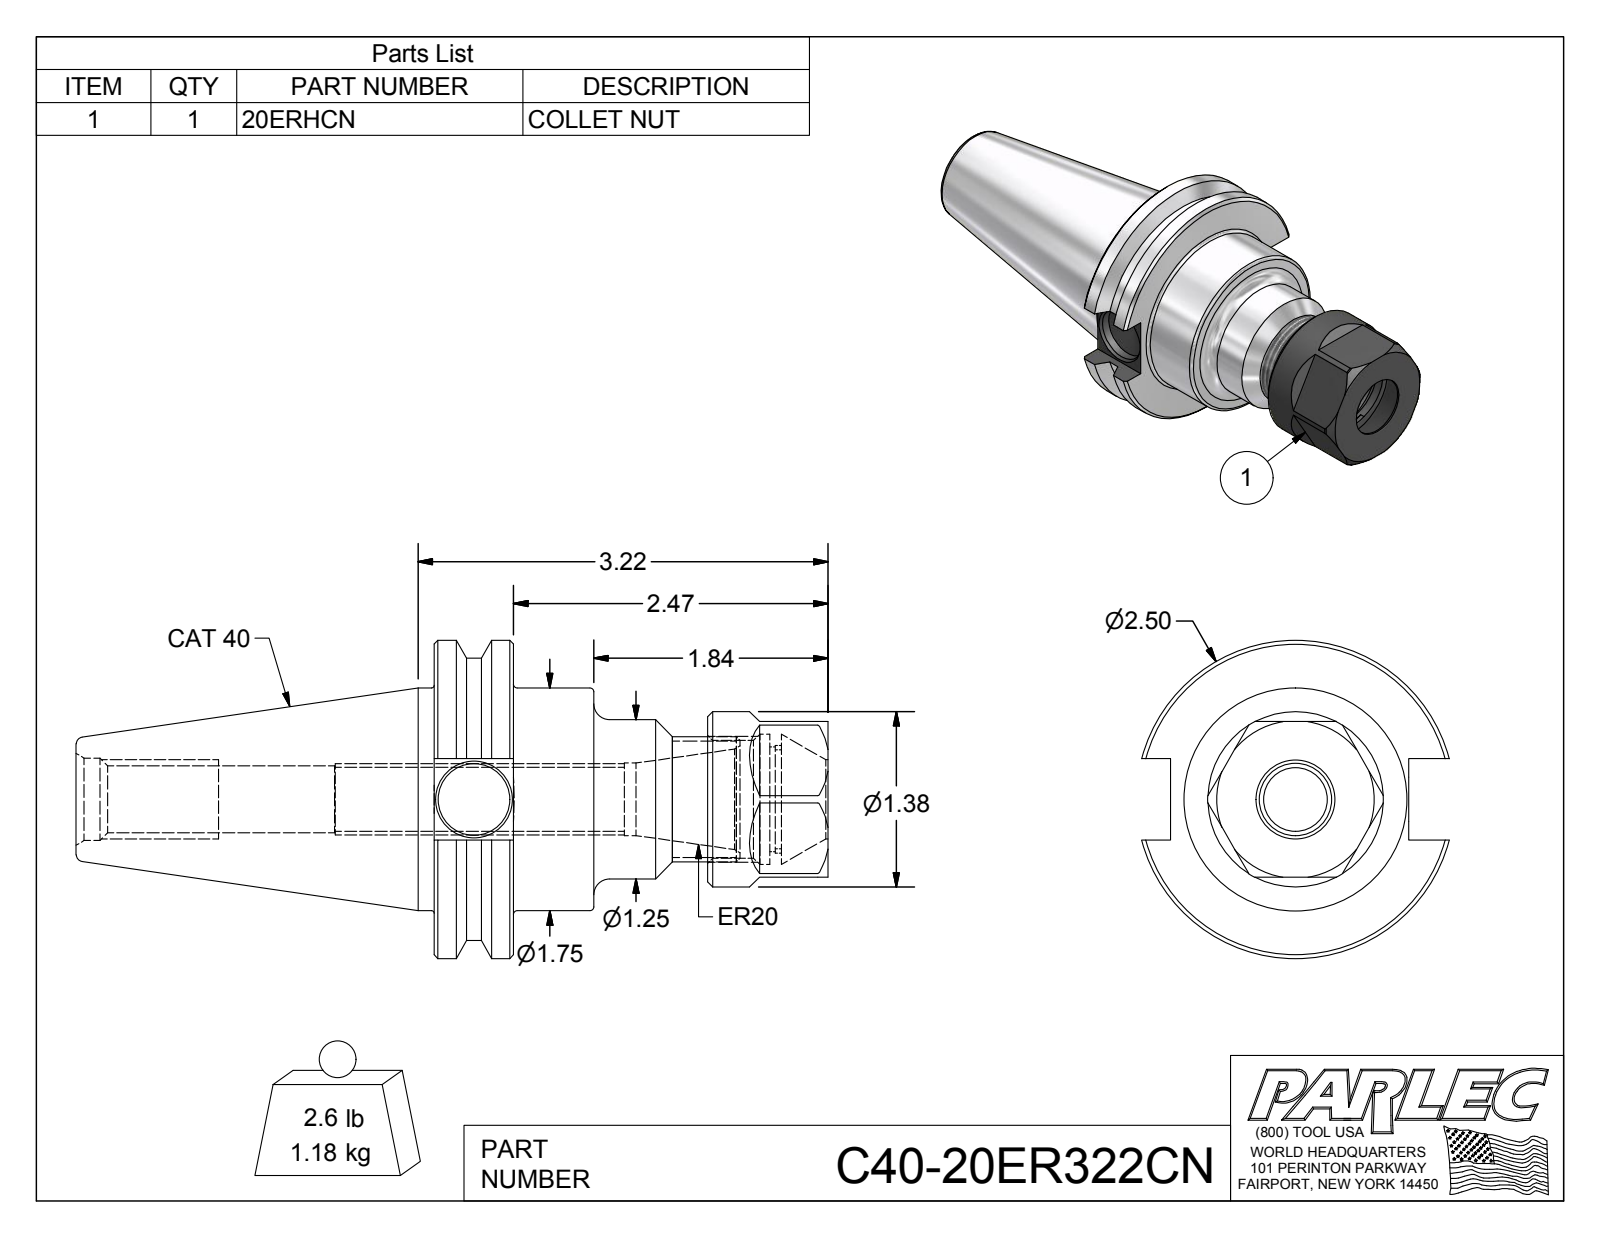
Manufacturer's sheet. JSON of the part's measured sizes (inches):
{"part_name": "C40-20ER322CN; C40-20ER3-1; 20ERHCN", "step_written_by": "Autodesk Inventor 2012 (AUTOMOTIVE_DESIGN)", "units": "inches", "bodies": {"solids": 2, "faces": 89, "planar": 29, "cylindrical": 21, "other": 39}, "overall_size": [5.908, 2.5, 2.417], "volume_in3": 9.019, "surface_area_in2": 49.87, "round_holes": [[0.502, 1], [0.527, 1], [0.563, 1], [0.57, 1], [0.62, 1], [0.648, 1], [0.82, 1], [0.925, 1], [1.024, 1]], "round_bosses_or_shafts": [[2.5, 1], [2.219, 1], [1.75, 1], [1.378, 1], [1.25, 1], [0.984, 1]], "partial_cylinders_radius": [[0.423, 1]], "face_to_face_distances": [0.625, 1.22, 3.095, 2.47, 0.29, 0.93, 2.15, 1.525, 0.945, 1.255], "hole_center_spacings": [0.037]}
